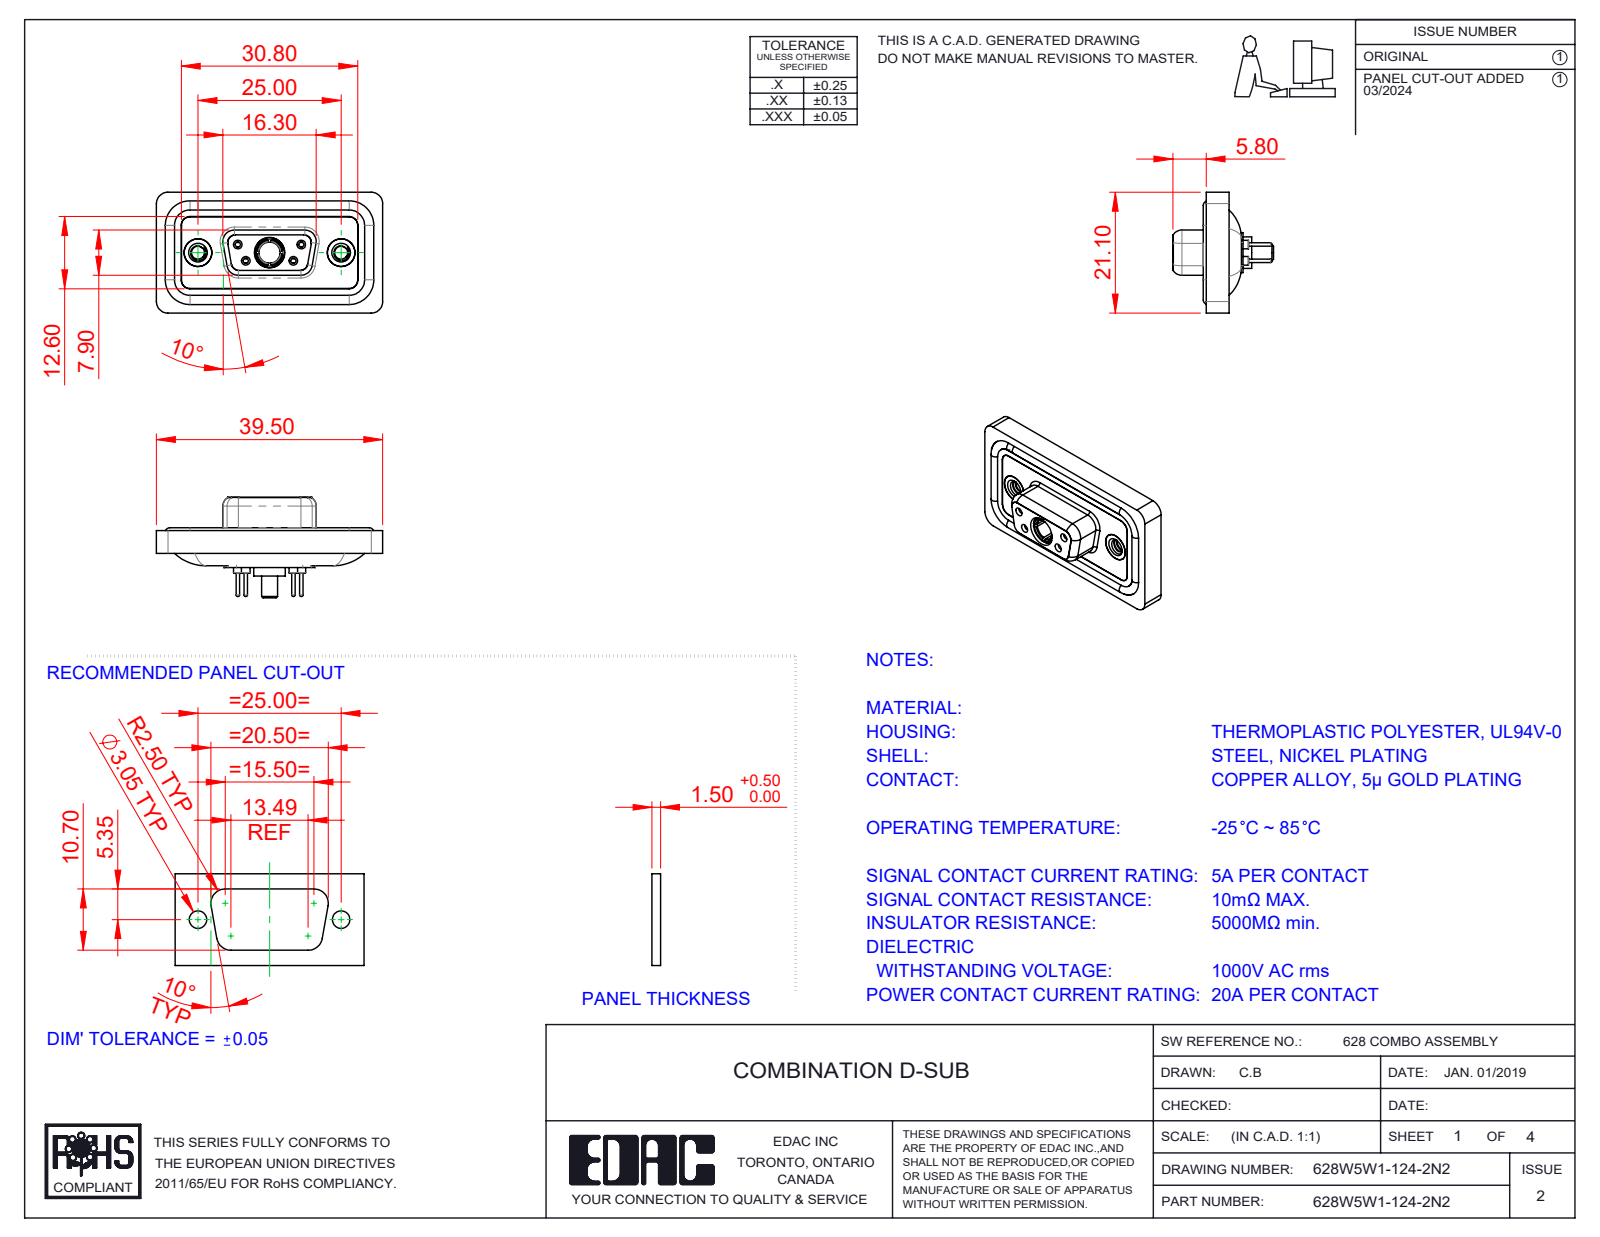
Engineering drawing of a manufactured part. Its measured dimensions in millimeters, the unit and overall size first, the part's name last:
Units: millimetres
Overall size (bounding box): 39.5 × 21.1 × 17.55
Round holes (diameter × count): ⌀0.9 ×4, ⌀1.1 ×4, ⌀1.5 ×4, ⌀2 ×4, ⌀4.85 ×3, ⌀1.6 ×2, ⌀1.7 ×2, ⌀2.26 ×2, ⌀4 ×2, ⌀4.05 ×2, ⌀5 ×2, ⌀3.7 ×1
Round bosses / shafts (diameter × count): ⌀1.6 ×6, ⌀2.2 ×4, ⌀0.6 ×4, ⌀4.95 ×2, ⌀4.8 ×2, ⌀5.5 ×1, ⌀5.2 ×1, ⌀4.96 ×1
Partial cylindrical surfaces — rounded edges, fillets, slot ends (radius × count): R1.5 ×22, R2 ×18, R1.35 ×8, R1.6 ×8, R0.25 ×4, R0.5 ×4, R0.6 ×4, R0.65 ×4
Main face-to-face distances: 0.4, 2.9, 1.1, 1.8, 1.6, 0.5, 5.65, 7.45, 5.35, 6.6
Hole centre spacings: 3.16, 5.72, 7.1, 12.5, 18.1, 4.39, 4.4, 8.31
Volume: 4 767 mm³ · Surface area: 7 635 mm²
Bodies: 13 solids, 680 faces (194 planar, 287 cylindrical, 199 other)
Part name (STEP PRODUCT): 628Combo Contact Row 1_24; 628Combo Shell Front_09 Contacts; 628Combo Threaded Rivet_2; 628Combo Shell Rear_09 Contacts (+5 more)
STEP written by: SolidWorks 2023 (CONFIG_CONTROL_DESIGN)
